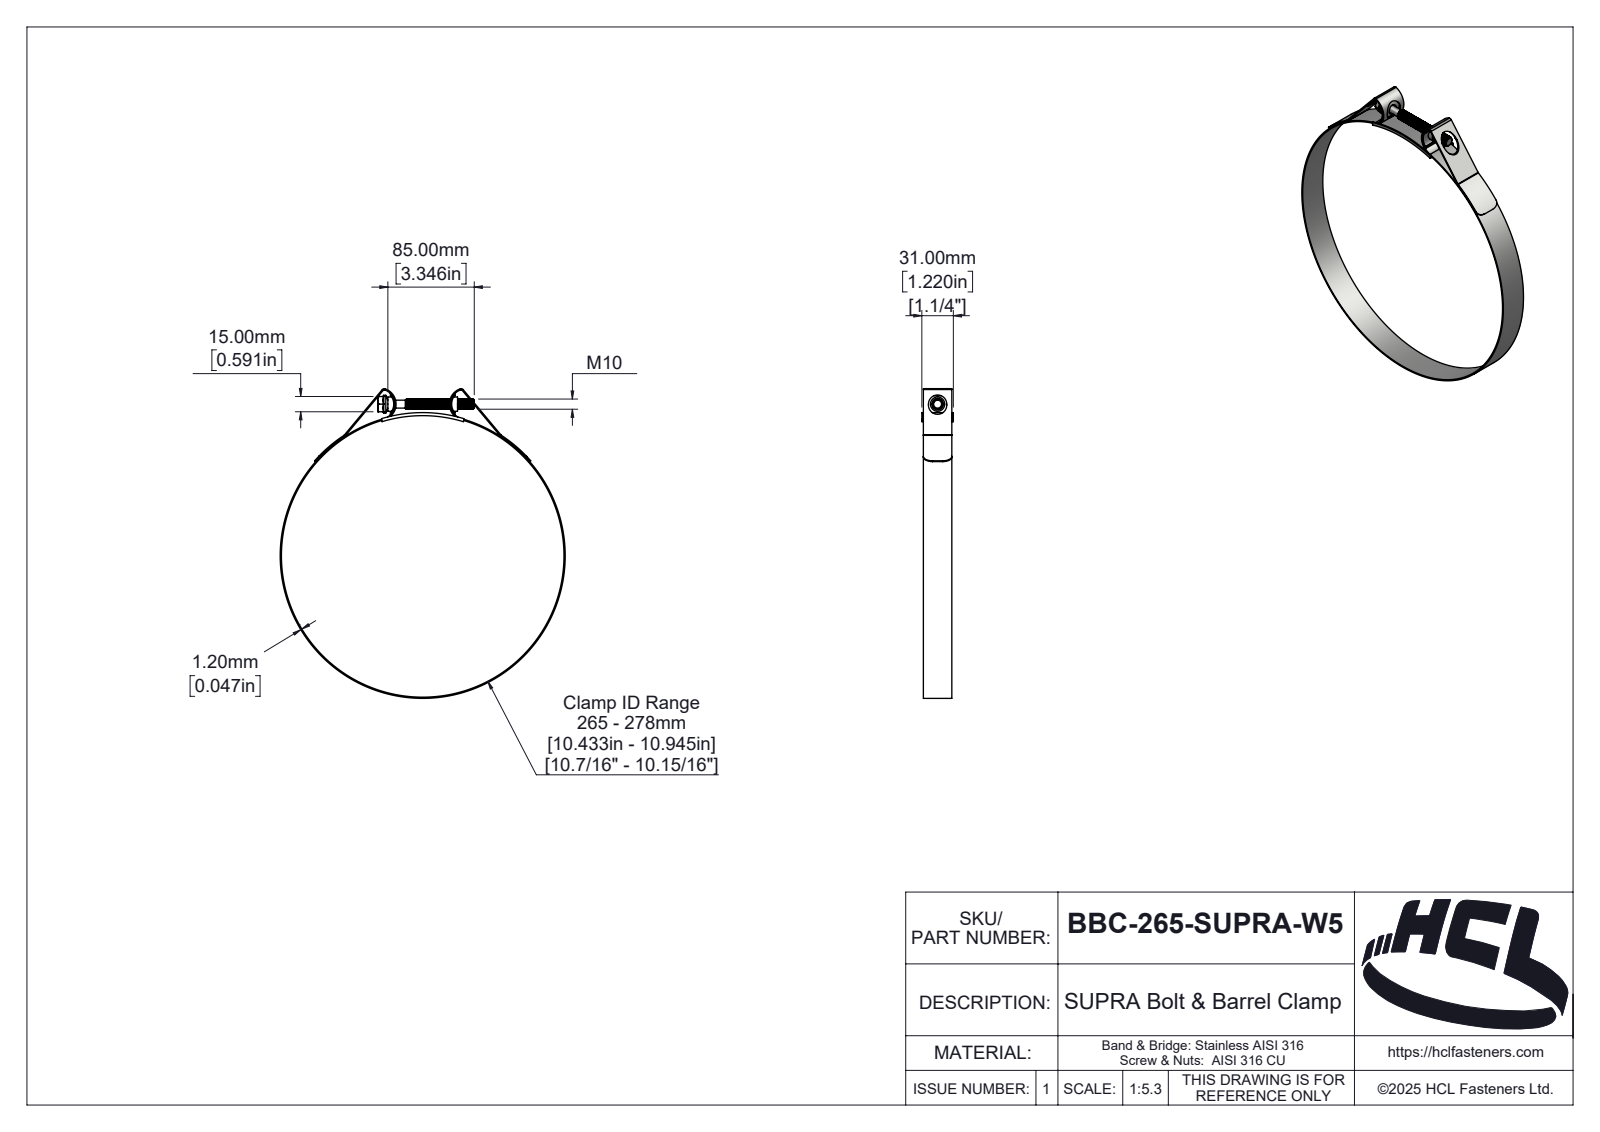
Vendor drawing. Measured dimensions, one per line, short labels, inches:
name: BBC-265-SUPRA-W5
written by: SolidWorks 2025 (AUTOMOTIVE_DESIGN)
unit: in
bodies: 5 solids, 380 faces (50 planar, 244 cylindrical, 86 other)
size: 11.991 × 11.039 × 1.22
volume: 2.886 in³; area: 115 in²
holes: 1× ⌀10.945
bosses: 1× ⌀11.039, 1× ⌀0.682, 1× ⌀0.551, 1× ⌀0.394, 1× ⌀0.307
rounds: 4× R0.039, 2× R0.051, 2× R0.079, 2× R0.098, 2× R0.126, 2× R0.354, 2× R0.538, 2× R0.577
face distances: 0.047, 1.102, 0.059, 1.161, 1.173, 1.114, 1.22, 1.126, 0.591, 0.098
